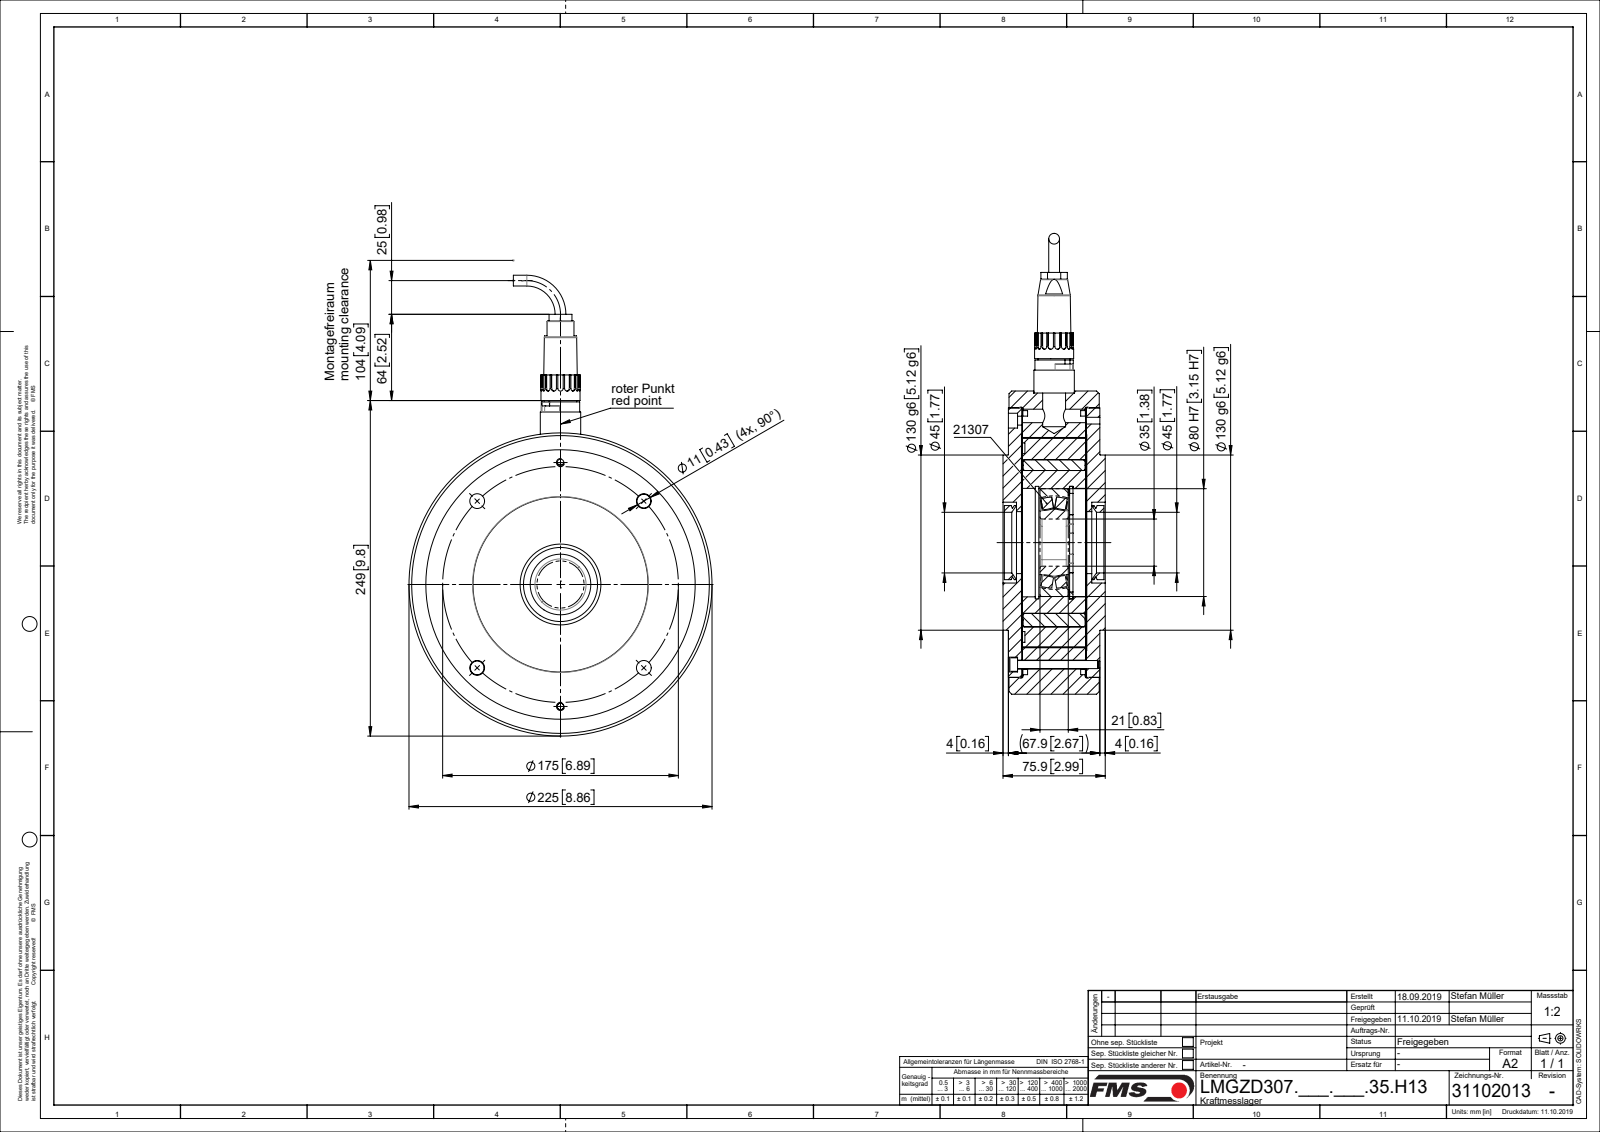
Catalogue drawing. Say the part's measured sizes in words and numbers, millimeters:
The part is named "49531_01; PRL_21307_01; Zyl-Schr DIN912_M6x60; 43404.02_01 (+8 more)". Its 3-D file was written by "SolidWorks 2018 (CONFIG_CONTROL_DESIGN)". It is 50 solids with 833 faces: 226 planar, 342 cylindrical and 265 other. Overall it measures 342 by 225 by 75.9 millimeters. Its volume is 2 469 000 cubic millimeters and its surface area 456 516 square millimeters. Round holes: 6 of diameter 11, 4 of diameter 2.5, 2 of diameter 3, 2 of diameter 3.4, 2 of diameter 3.6, 2 of diameter 5, 2 of diameter 6.6, 2 of diameter 10, 2 of diameter 10.2, 1 of diameter 8, 1 of diameter 10.5, 1 of diameter 14. Round bosses or shafts: 7 of diameter 2.15, 2 of diameter 5.5, 2 of diameter 3, 1 of diameter 225, 1 of diameter 199, 1 of diameter 188, 1 of diameter 140, 1 of diameter 132. Partial cylindrical surfaces (rounded edges, fillets, slot ends): 17 of radius 2, 4 of radius 0.1, 4 of radius 11, 2 of radius 3, 2 of radius 4.91, 1 of radius 33.25, 1 of radius 79, 1 of radius 82. The main face-to-face distances are 47.25, 48, 0.75, 0.5, 47.75, 9.7, 10.2, 10.45, 57.45, 57.7. The hole center spacings are 16.26, 22.47, 23, 62.02, 68.17, 87.5, 123.74, 134.45.
